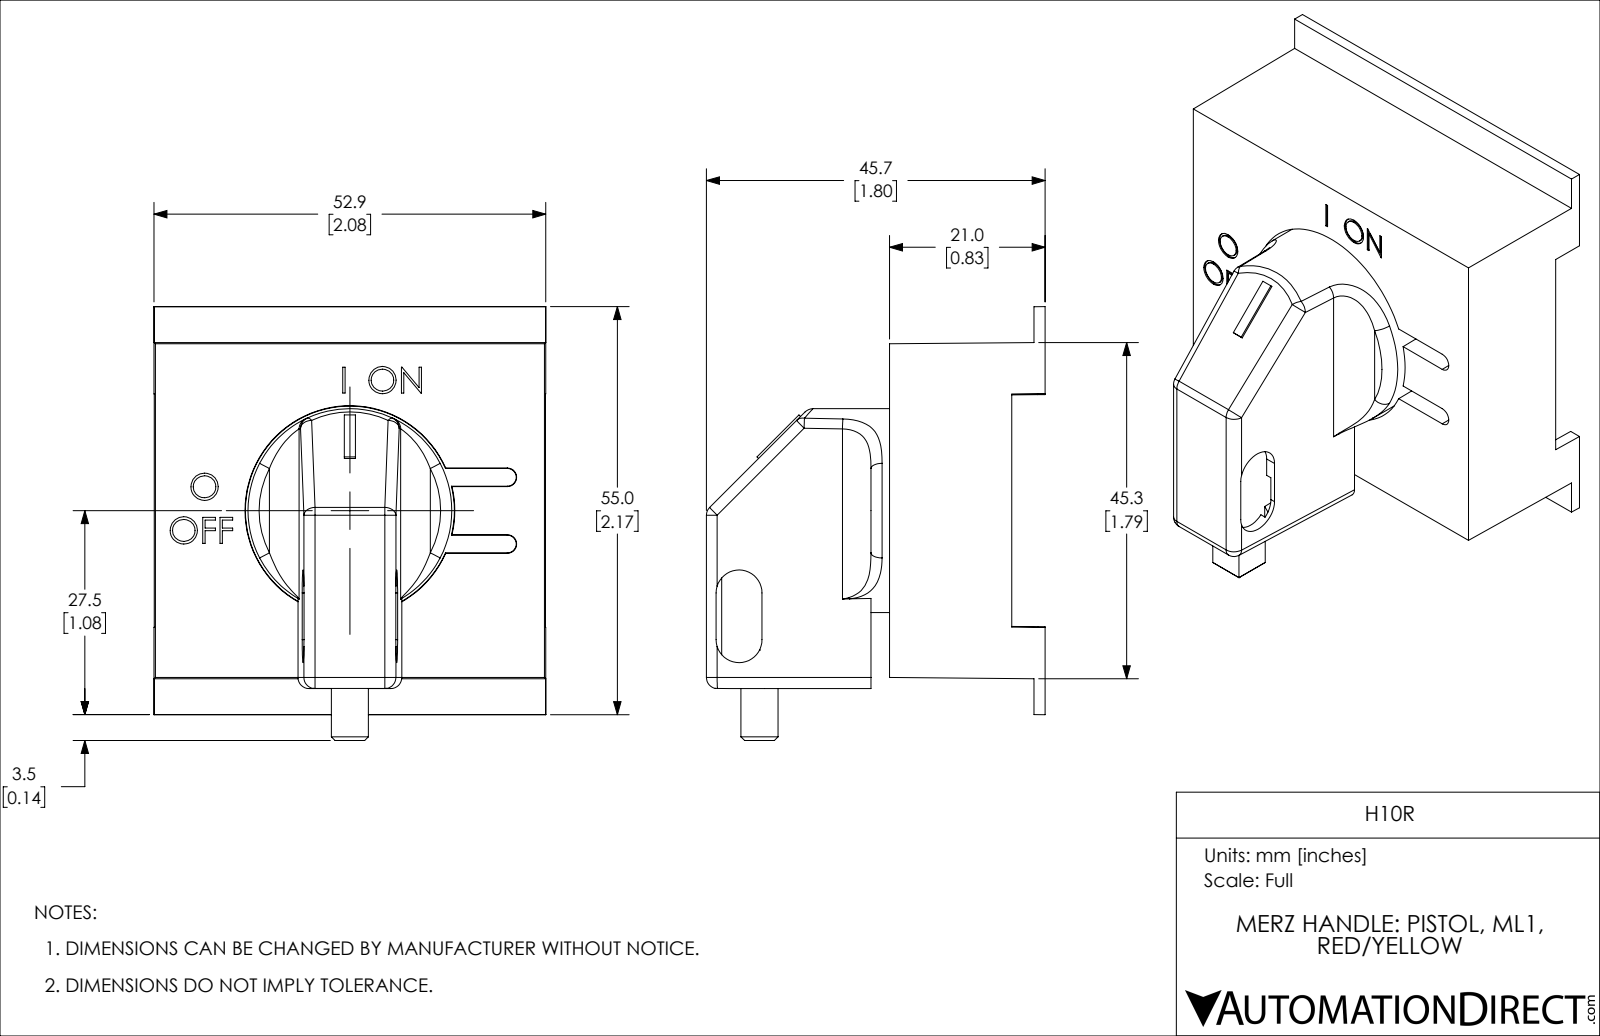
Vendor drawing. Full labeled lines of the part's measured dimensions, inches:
Part name (STEP PRODUCT): H10R
STEP written by: SolidWorks 2019 (AUTOMOTIVE_DESIGN)
Units: inches
Bodies: 1 solid, 339 faces (225 planar, 42 cylindrical, 72 other)
Overall size (bounding box): 2.304 × 2.081 × 1.799
Volume: 1.535 in³ · Surface area: 32.45 in²
Round bosses / shafts (diameter × count): ⌀1.083 ×1, ⌀0.906 ×1
Partial cylindrical surfaces — rounded edges, fillets, slot ends (radius × count): R0.012 ×8, R0.059 ×8, R0.039 ×4, R0.02 ×3, R0.122 ×2, R0.157 ×2
Main face-to-face distances: 0.047, 0.094, 0.067, 0.059, 0.827, 0.531, 0.732, 0.492, 0.039, 0.419
